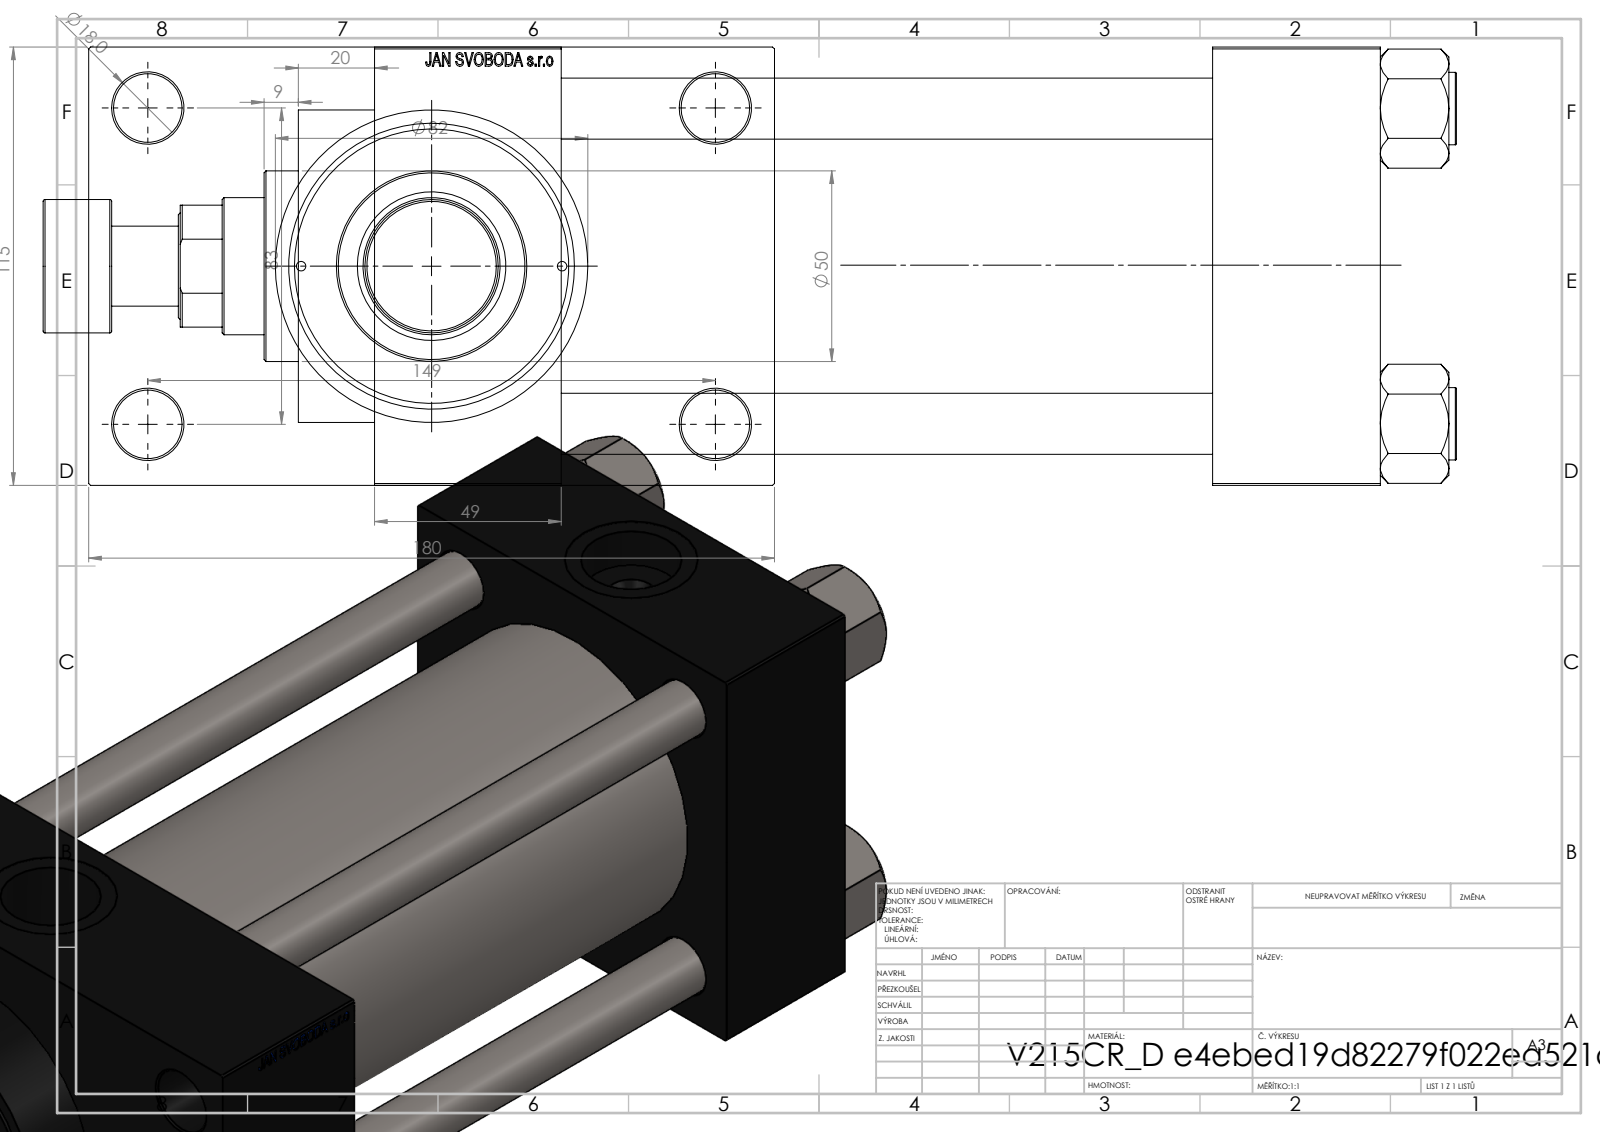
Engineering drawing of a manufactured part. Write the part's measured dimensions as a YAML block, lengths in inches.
part_name: "V215CR_D_TYCINKA; V215_VC_A; V215CR_VCP_D; NUT_M5_D (+2 more)"
step_written_by: "SolidWorks 2019 (CONFIG_CONTROL_DESIGN)"
units: inches
bodies: {solids: 12, faces: 1174, planar: 551, cylindrical: 97, other: 526}
overall_size: [14.606, 7.087, 4.528]
volume: 140
surface_area: 600
round_holes:
  - {diameter: 0.63, count: 4}
  - {diameter: 0.709, count: 4}
  - {diameter: 0.098, count: 2}
  - {diameter: 0.276, count: 2}
  - {diameter: 1.041, count: 2}
  - {diameter: 1.378, count: 2}
  - {diameter: 1.004, count: 1}
  - {diameter: 1.417, count: 1}
  - {diameter: 1.535, count: 1}
  - {diameter: 2.402, count: 1}
  - {diameter: 2.835, count: 1}
  - {diameter: 3.15, count: 1}
round_bosses_or_shafts:
  - {diameter: 0.748, count: 4}
  - {diameter: 3.386, count: 1}
  - {diameter: 3.228, count: 1}
  - {diameter: 1.969, count: 1}
  - {diameter: 1.378, count: 1}
  - {diameter: 0.827, count: 1}
face_to_face_distances: [4.528, 6.732, 1.929, 8.661, 1.732, 8.465, 10.394, 1.28, 5.807, 7.087]
hole_center_spacings: [1.305, 1.652, 2.276, 2.302, 3.256, 3.357, 3.393, 3.513]
